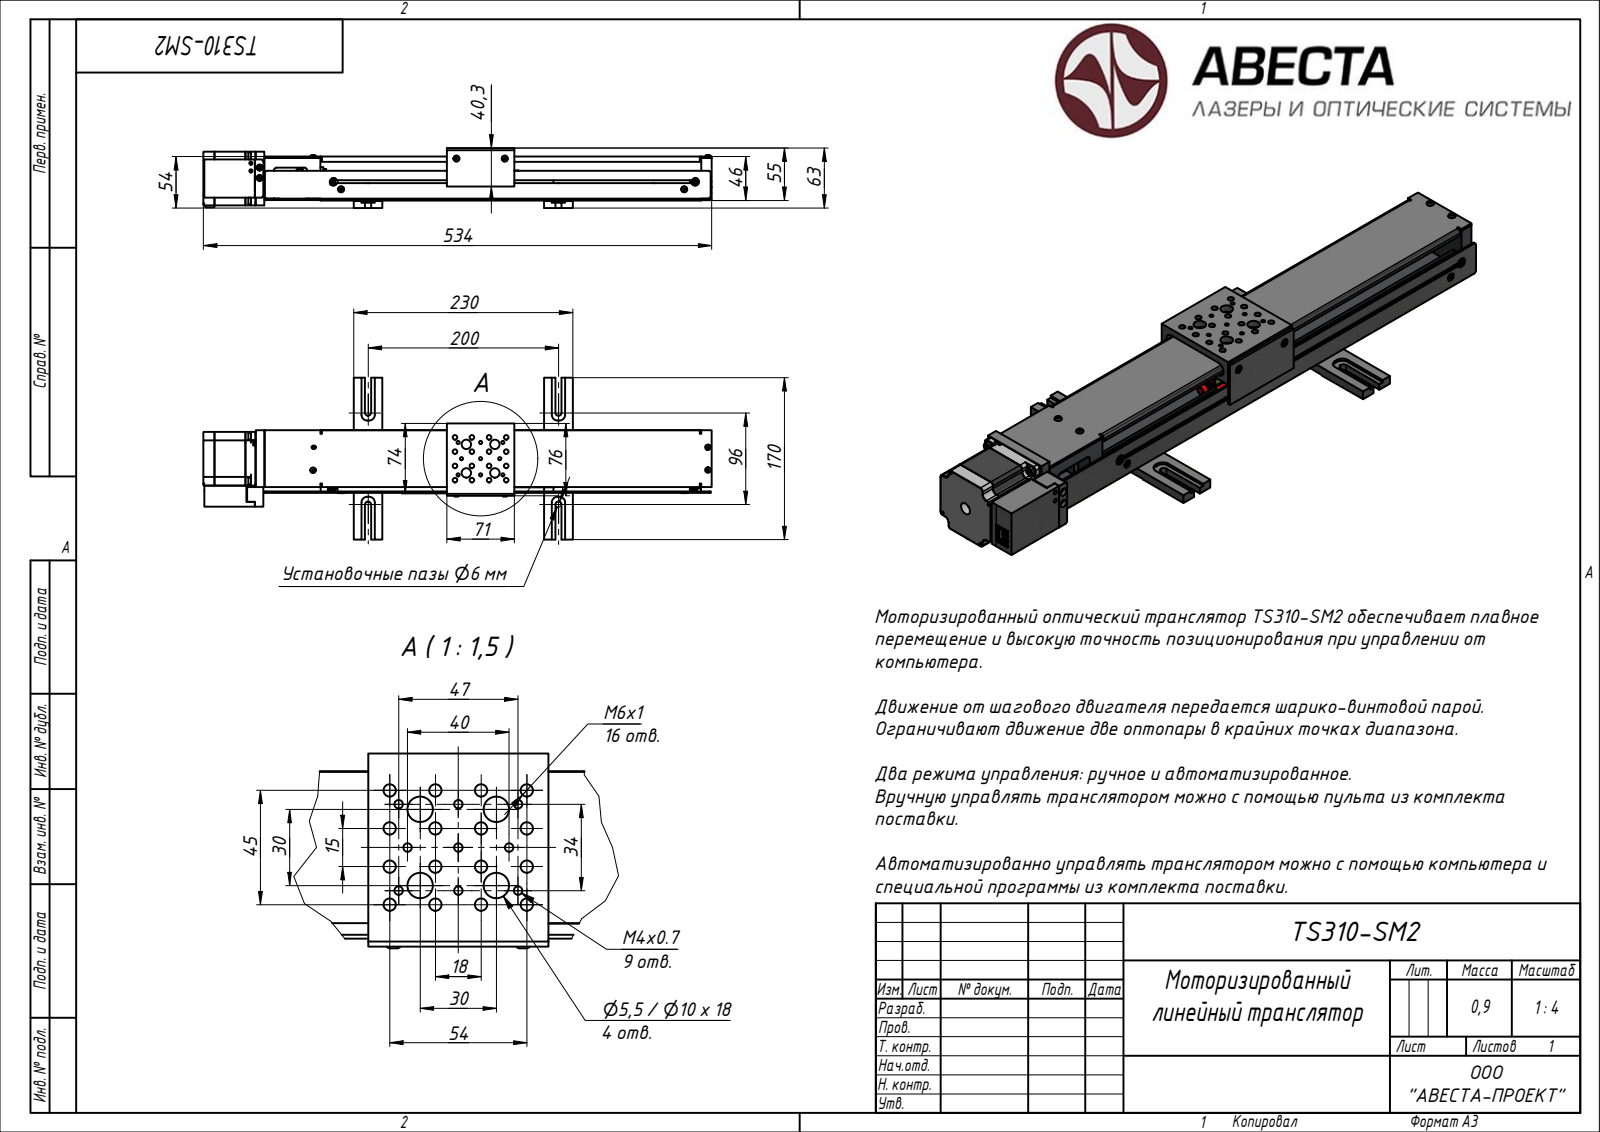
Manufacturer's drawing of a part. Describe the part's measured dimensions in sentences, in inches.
Its 3-D file was written by "Rhino 7.34 (AUTOMOTIVE_DESIGN)". It is 1 solid with 2206 faces: 864 planar, 763 cylindrical and 579 other. Overall it measures 21.02 by 6.693 by 2.48 inches. Its volume is 55.72 cubic inches and its surface area 478.4 square inches. Round holes: 17 of diameter 0.128, 14 of diameter 0.134, 12 of diameter 0.217, 11 of diameter 0.194, 8 of diameter 0.163, 8 of diameter 0.256, 8 of diameter 0.374, 6 of diameter 0.097, 5 of diameter 0.194, 5 of diameter 0.394, 4 of diameter 0.064, 4 of diameter 0.08. Round bosses or shafts: 10 of diameter 0.217, 7 of diameter 0.236, 6 of diameter 0.276, 6 of diameter 0.224, 4 of diameter 0.157, 4 of diameter 0.079, 2 of diameter 0.118, 1 of diameter 1.5. Partial cylindrical surfaces (rounded edges, fillets, slot ends): 30 of radius 0.118, 16 of radius 0.098, 15 of radius 0.079, 12 of radius 0.059, 10 of radius 0.236, 8 of radius 0.02, 7 of radius 0.039, 7 of radius 0.276. The main face-to-face distances are 0.059, 0.02, 0.295, 0.315, 0.354, 1.791, 0.276, 1.752, 1.732, 1.457. The hole center spacings are 1.181, 3.937, 7.874, 7.962, 4.11, 0.276, 0.28, 0.344.
